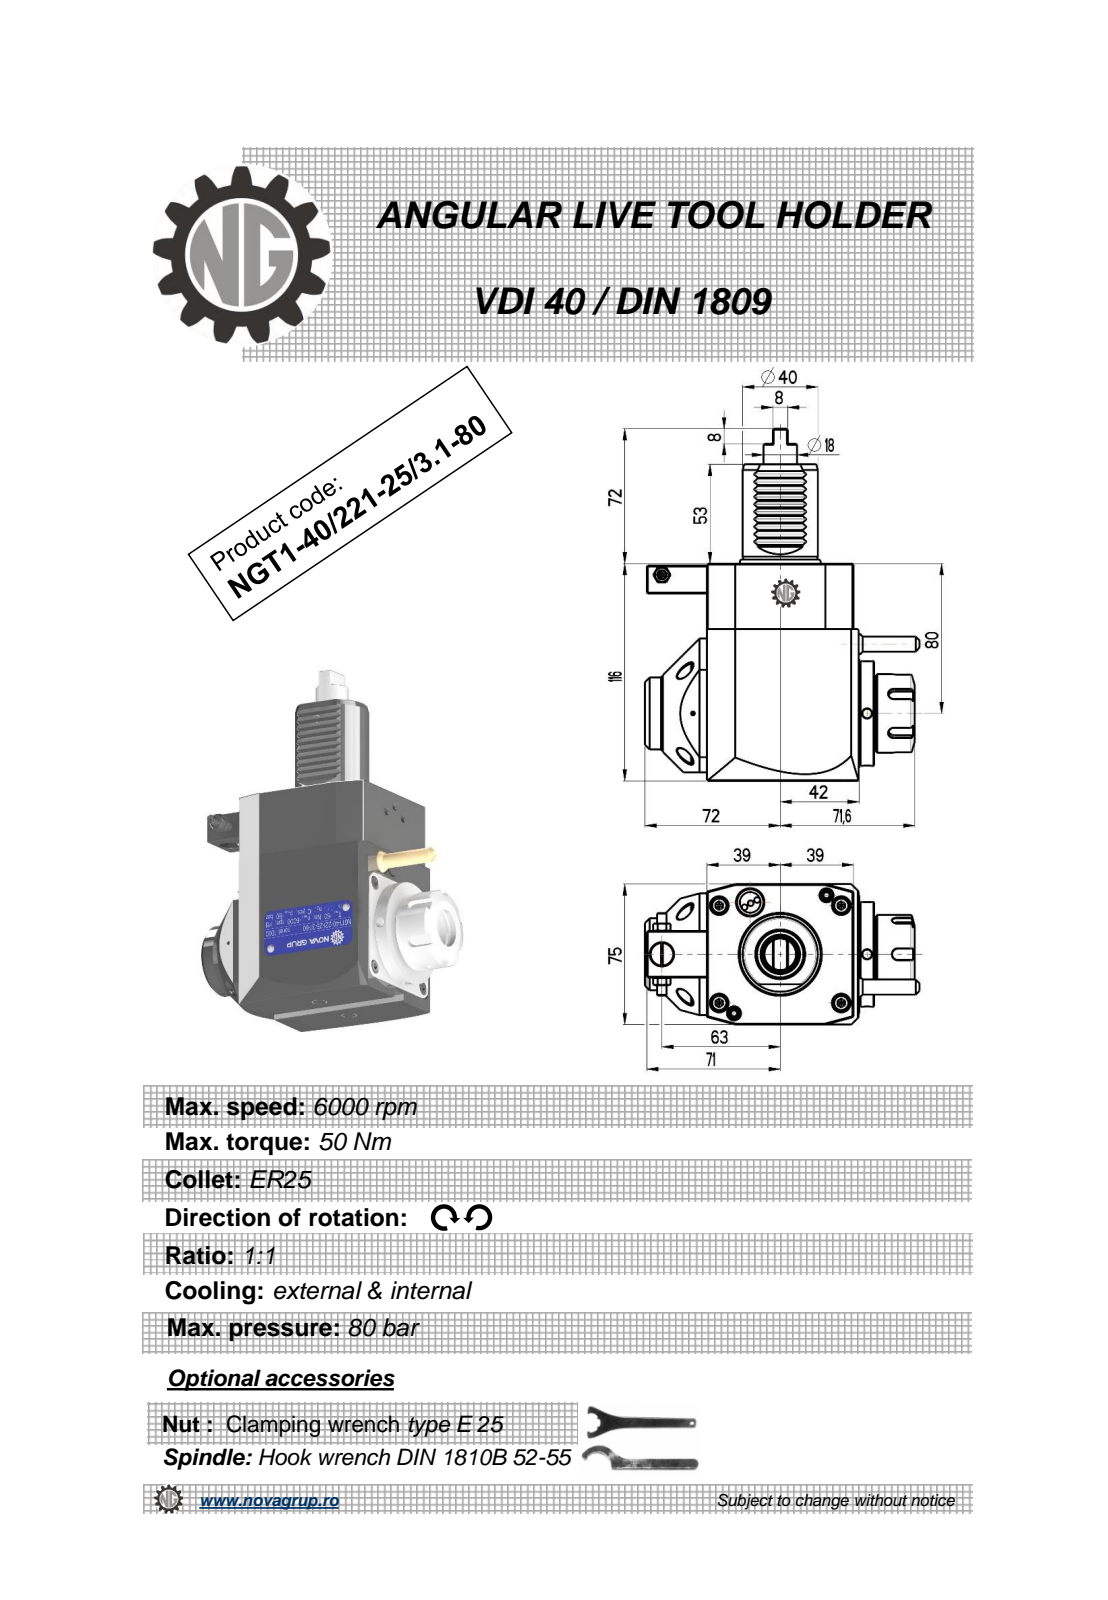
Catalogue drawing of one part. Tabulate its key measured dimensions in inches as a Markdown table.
| quantity | value |
| --- | --- |
| part name | NGT1_40_221_25_3_1_80 |
| STEP written by | PRO/ENGINEER BY PARAMETRIC TECHNOLOGY CORPORATION, 2010280 (CONFIG_CONTROL_DESIGN) |
| units | inches |
| bodies | 1 solid, 427 faces (193 planar, 87 cylindrical, 147 other) |
| overall size | 7.402 × 5.754 × 2.953 |
| volume | 54.11 in³ |
| surface area | 110.9 in² |
| round holes (diameter × count) | 0.197 × 3, 0.118 × 1, 0.165 × 1, 0.374 × 1, 0.472 × 1, 0.799 × 1 |
| round bosses / shafts (diameter × count) | 2.205 × 1, 1.693 × 1, 1.654 × 1, 1.575 × 1, 1.516 × 1, 1.299 × 1, 0.701 × 1, 0.441 × 1 |
| partial cylindrical surfaces (radius × count) | 0.01 × 12, 0.012 × 10, 0.009 × 6, 0.118 × 5, 0.031 × 2, 0.02 × 1, 1.575 × 1 |
| main face-to-face distances | 2.953, 4.567, 3.189, 3.071, 0.118, 0.315, 0.433, 4.37, 3.181, 0.11 |
| hole center spacings | 1.558, 1.611, 2.854, 4.301, 5.195 |
